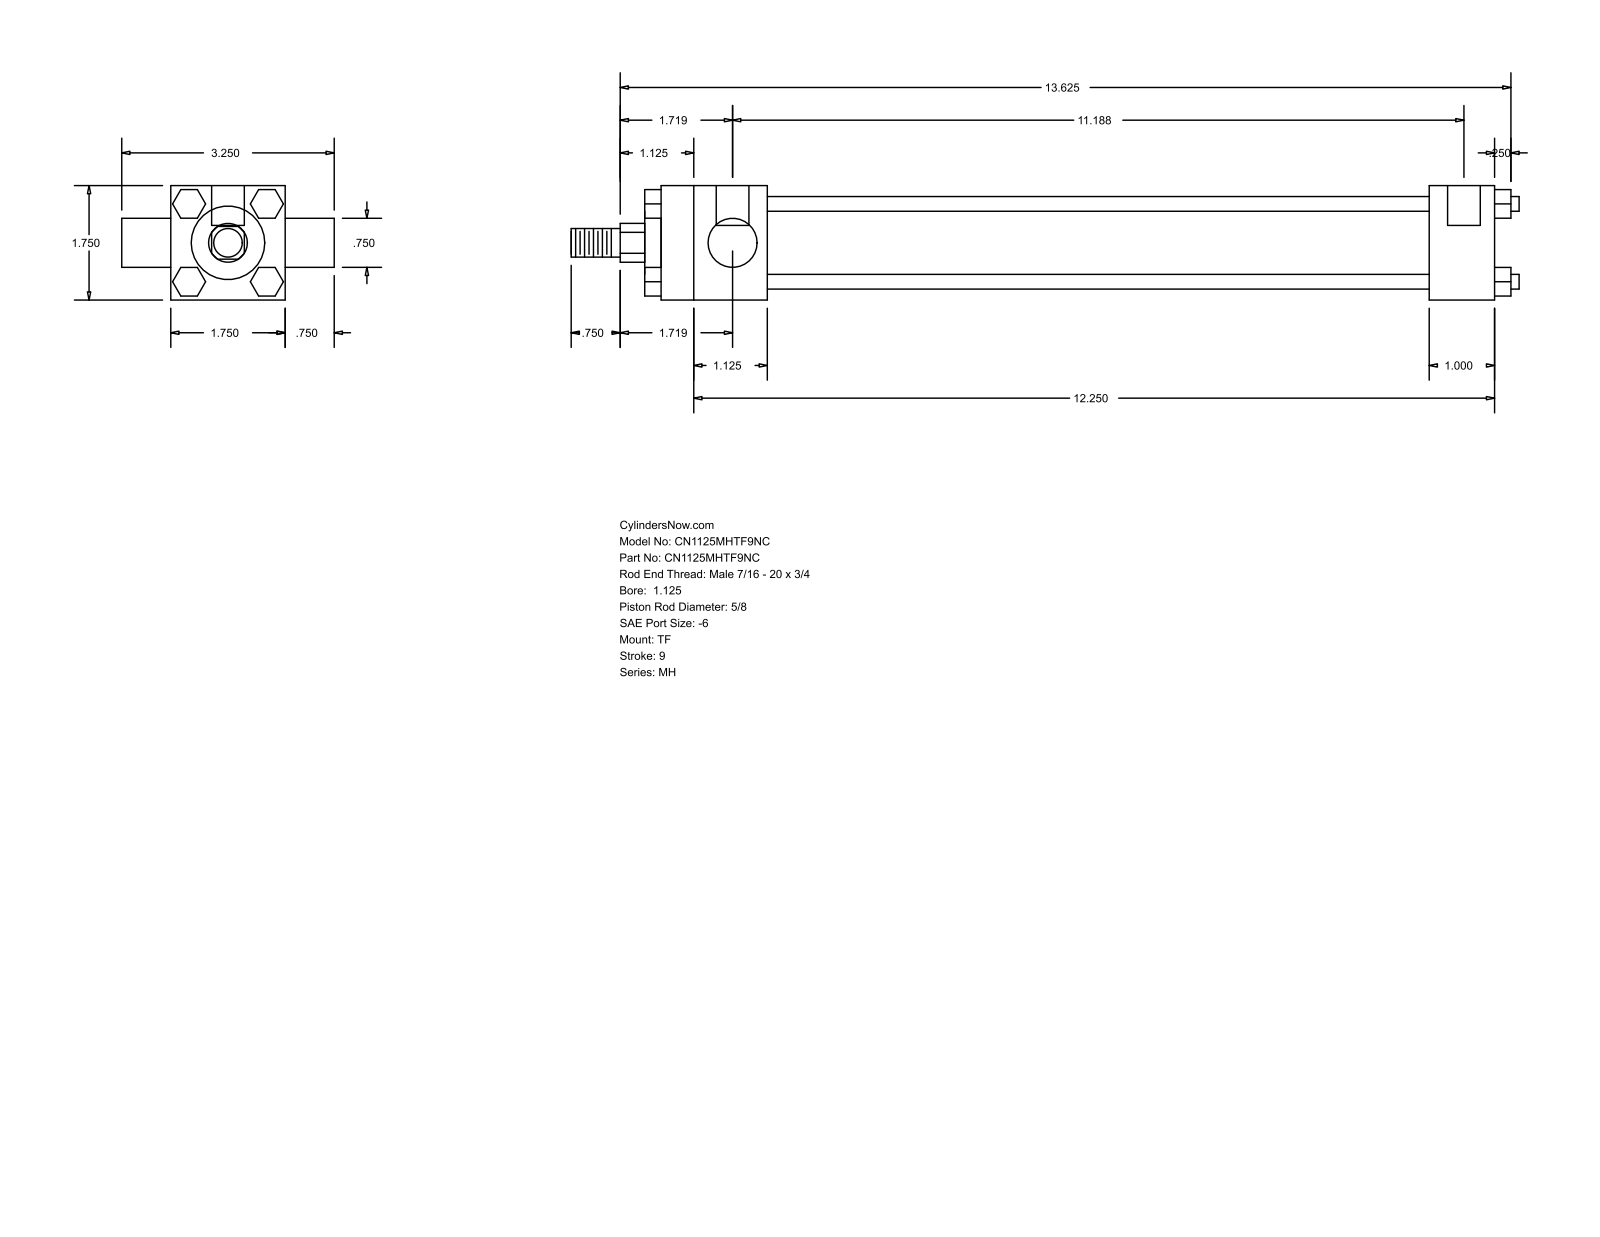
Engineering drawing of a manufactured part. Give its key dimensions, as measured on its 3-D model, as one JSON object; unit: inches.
{"part_name": "MH_TF__0112_0.625", "step_written_by": "GSSL Pune (CONFIG_CONTROL_DESIGN)", "units": "inches", "bodies": {"solids": 0, "faces": 120, "planar": 92, "cylindrical": 28, "other": 0}, "overall_size": [14.5, 3.25, 1.75], "round_holes": [[0.219, 3], [0.5, 2]], "round_bosses_or_shafts": [[0.225, 4], [1.375, 1], [1.125, 1], [0.75, 1], [0.625, 1], [0.437, 1]], "partial_cylinders_radius": [[0.297, 1]], "face_to_face_distances": [1.75, 0.437, 10.125, 11.125, 1, 1.625, 11.75, 12.75, 1.875, 0.25], "hole_center_spacings": [0.125, 11.063, 11.187]}
